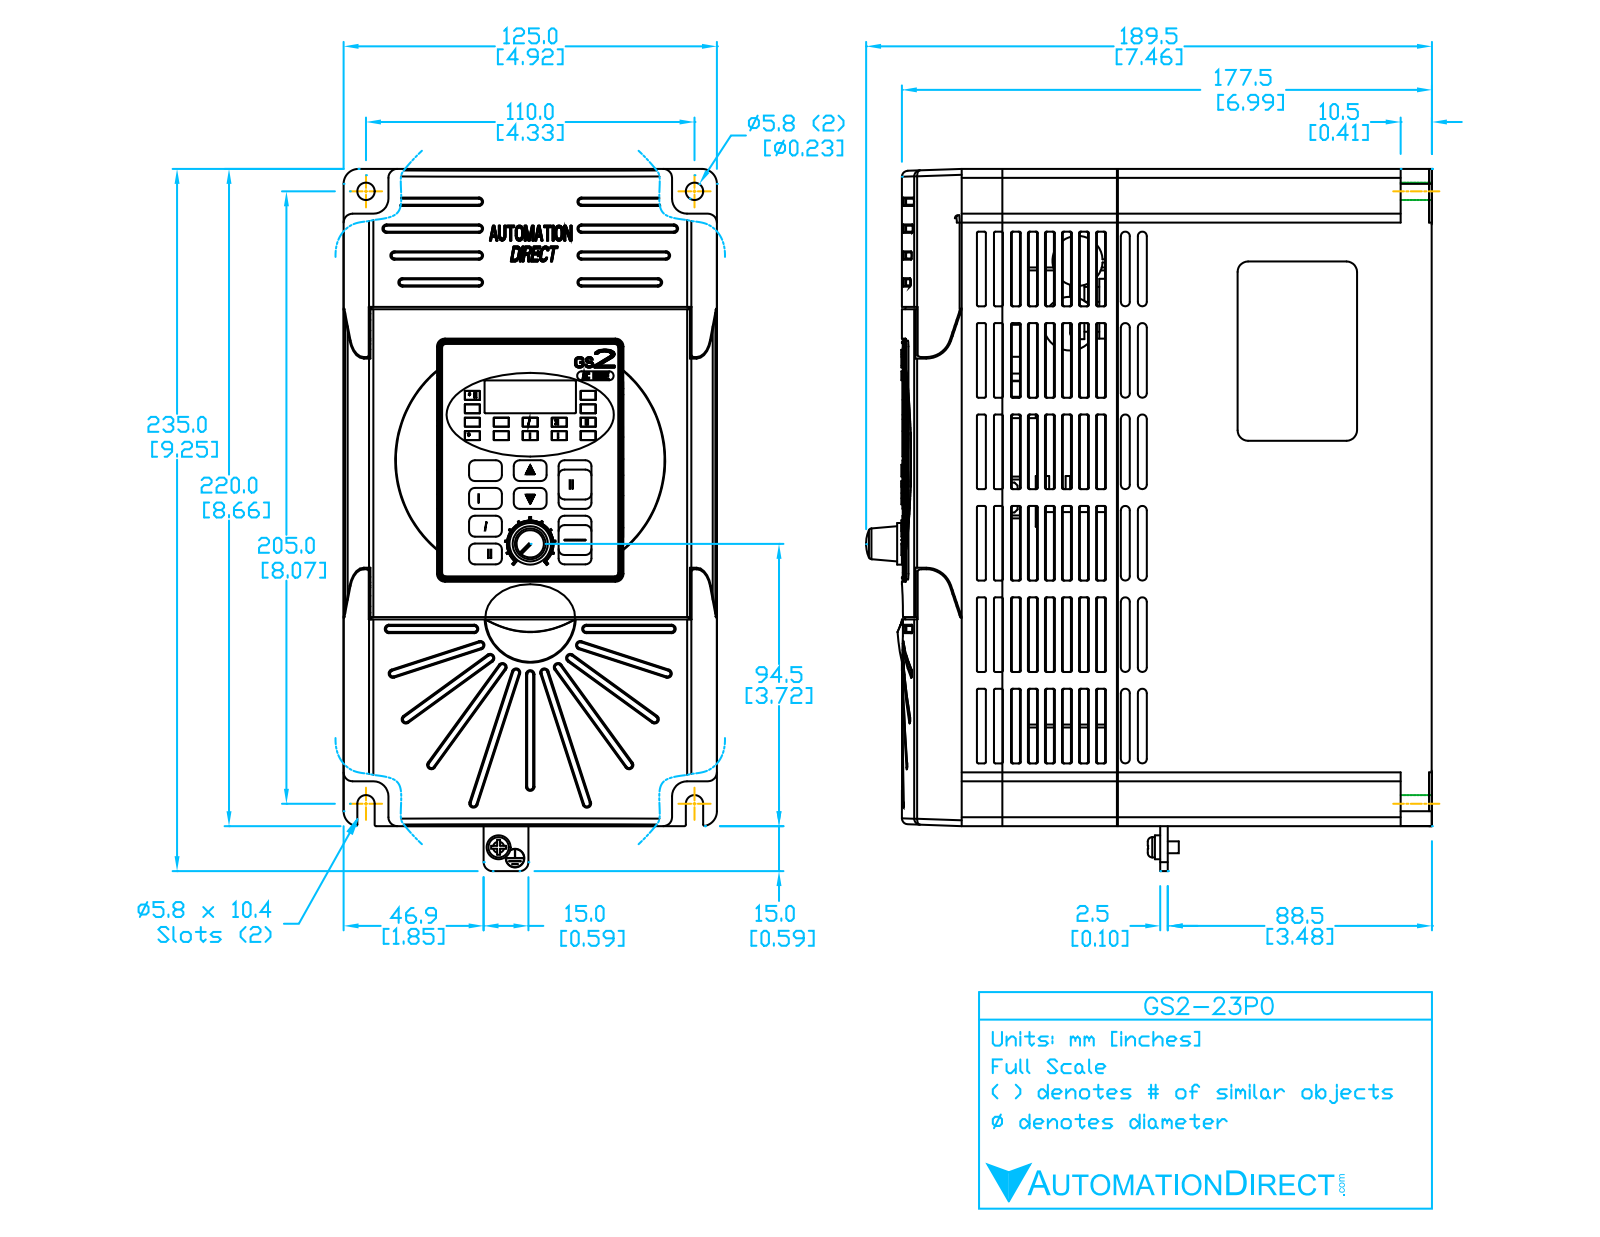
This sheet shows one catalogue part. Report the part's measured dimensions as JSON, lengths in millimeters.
{"part_name": "GS2-23P0", "step_written_by": "SolidWorks 2013 (AUTOMOTIVE_DESIGN)", "units": "millimeters", "bodies": {"solids": 1, "faces": 797, "planar": 344, "cylindrical": 218, "other": 235}, "overall_size": [235, 190.1, 125], "volume_mm3": 4636000, "surface_area_mm2": 226300, "round_holes": [[5.8, 2], [81.3, 1]], "round_bosses_or_shafts": [[13.8, 1], [6.6, 1], [3.8, 1]], "partial_cylinders_radius": [[1.5, 40], [1, 38], [3.2, 12], [5.1, 8], [0.5, 6], [1.6, 6], [6.4, 6], [2.5, 4]], "face_to_face_distances": [0.4, 124.6, 125, 157, 219.6, 124.2, 220, 156.7, 14.7, 14.4], "hole_center_spacings": [110]}
